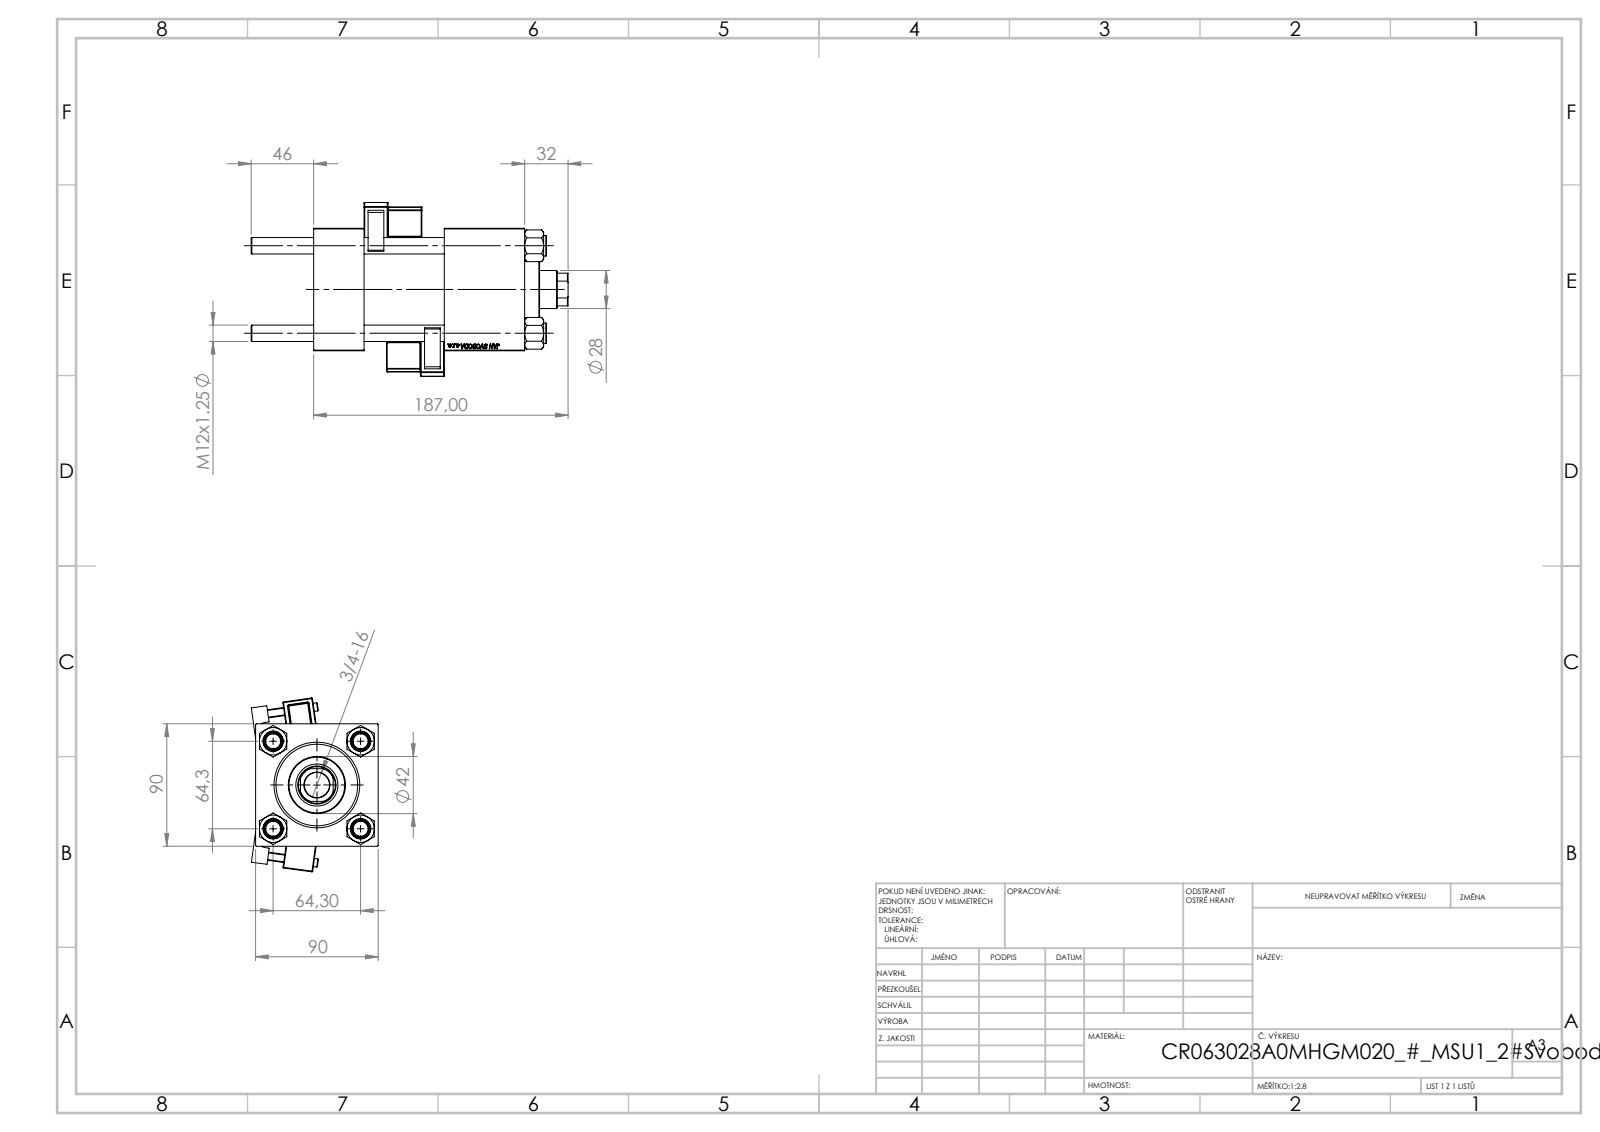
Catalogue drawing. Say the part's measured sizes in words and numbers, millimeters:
The part is named "V215_VC_A; V215CR_VCP; NUT_M5; CR025_012_A_0_G_A_G_M_020_+#_##_TYCINKA (+2 more)". Its 3-D file was written by "SolidWorks 2019 (CONFIG_CONTROL_DESIGN)". It is 13 solids with 1288 faces: 578 planar, 138 cylindrical and 572 other. Overall it measures 233 by 127.75 by 93.19 millimeters. Its volume is 1 022 000 cubic millimeters and its surface area 207 533 square millimeters. Round holes: 4 of diameter 12, 2 of diameter 7, 2 of diameter 20.96, 2 of diameter 30, 1 of diameter 18.5, 1 of diameter 28, 1 of diameter 31, 1 of diameter 50, 1 of diameter 60, 1 of diameter 63. Round bosses or shafts: 4 of diameter 15, 2 of diameter 6, 1 of diameter 69, 1 of diameter 42. Partial cylindrical surfaces (rounded edges, fillets, slot ends): 48 of radius 0.5, 2 of radius 1, 2 of radius 2.5, 2 of radius 4, 1 of radius 13.5. The main face-to-face distances are 90, 59, 37, 155, 118, 96, 126.3, 89.3, 30.3, 28.7. The hole center spacings are 45.47, 64.3, 90.93, 97.5.
